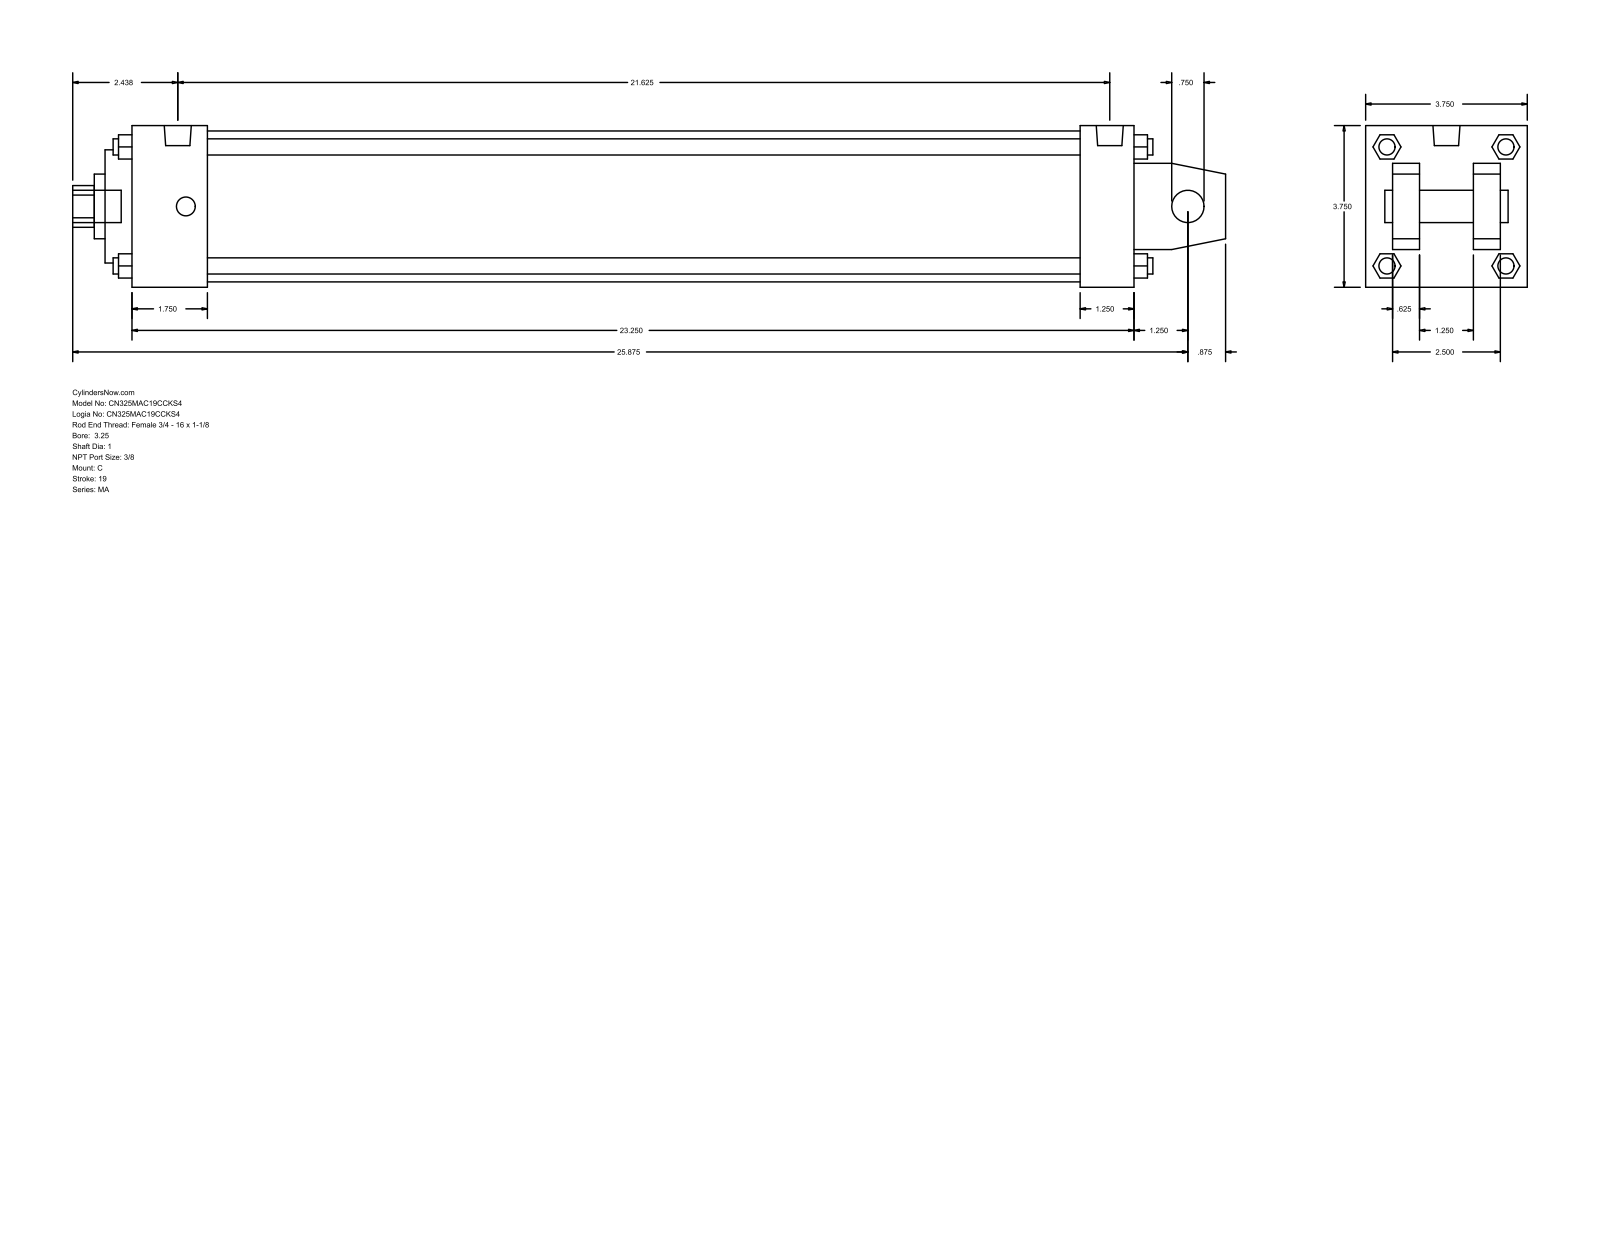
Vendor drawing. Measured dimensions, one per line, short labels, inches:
name: MA_C__0325_1
written by: GSSL Pune (CONFIG_CONTROL_DESIGN)
unit: in
bodies: 0 solids, 141 faces (109 planar, 32 cylindrical, 0 other)
size: 26.75 × 3.75 × 3.75
holes: 1× ⌀0.75, 1× ⌀1, 1× ⌀1.5, 1× ⌀2.625, 1× ⌀3.5
bosses: 4× ⌀0.437, 4× ⌀0.375, 2× ⌀0.627, 1× ⌀0.75
rounds: 1× R0.484
face distances: 3.75, 0.625, 2.5, 23.25, 1.25, 3.125, 1.875, 22, 1.25, 1.75
